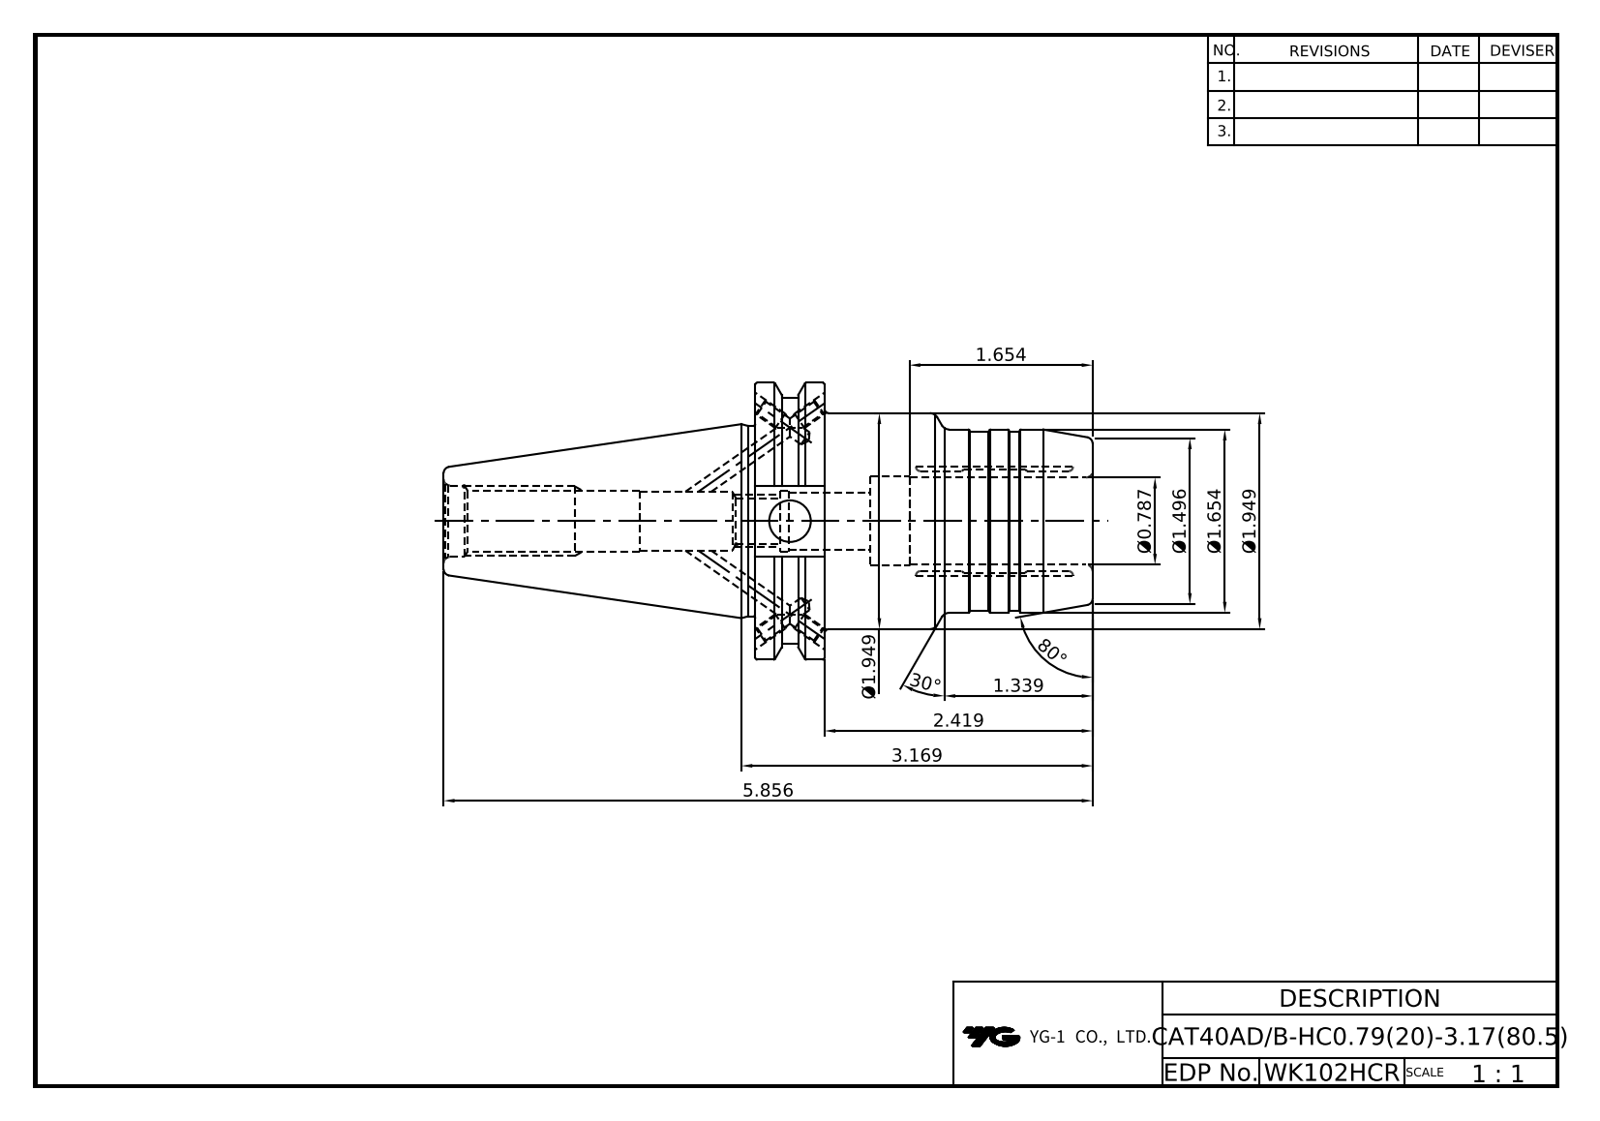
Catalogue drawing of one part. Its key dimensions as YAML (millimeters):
part_name: "LO-CAT40ADB-HCR20-80.5"
step_written_by: "Autodesk Inventor 2020 (AUTOMOTIVE_DESIGN)"
units: millimeters
bodies: {solids: 1, faces: 106, planar: 34, cylindrical: 35, other: 37}
overall_size: [148.75, 63.5, 61.09]
volume: 180698
surface_area: 32772
round_holes:
  - {diameter: 3.24, count: 4}
  - {diameter: 4, count: 4}
  - {diameter: 9.53, count: 1}
  - {diameter: 10.11, count: 1}
  - {diameter: 13, count: 1}
  - {diameter: 13.39, count: 1}
  - {diameter: 14, count: 1}
  - {diameter: 16.3, count: 1}
  - {diameter: 20, count: 1}
  - {diameter: 20.4, count: 1}
round_bosses_or_shafts:
  - {diameter: 63.5, count: 1}
  - {diameter: 56.3, count: 1}
  - {diameter: 49.5, count: 1}
  - {diameter: 43.6, count: 1}
  - {diameter: 42, count: 1}
  - {diameter: 41, count: 1}
partial_cylinders:
  - {radius: 8.19, count: 1}
face_to_face_distances: [15.88, 77.33, 61.45, 26.33, 10.45, 51, 47.6, 16.38, 71.42, 87.3]
hole_center_spacings: [35.13]
